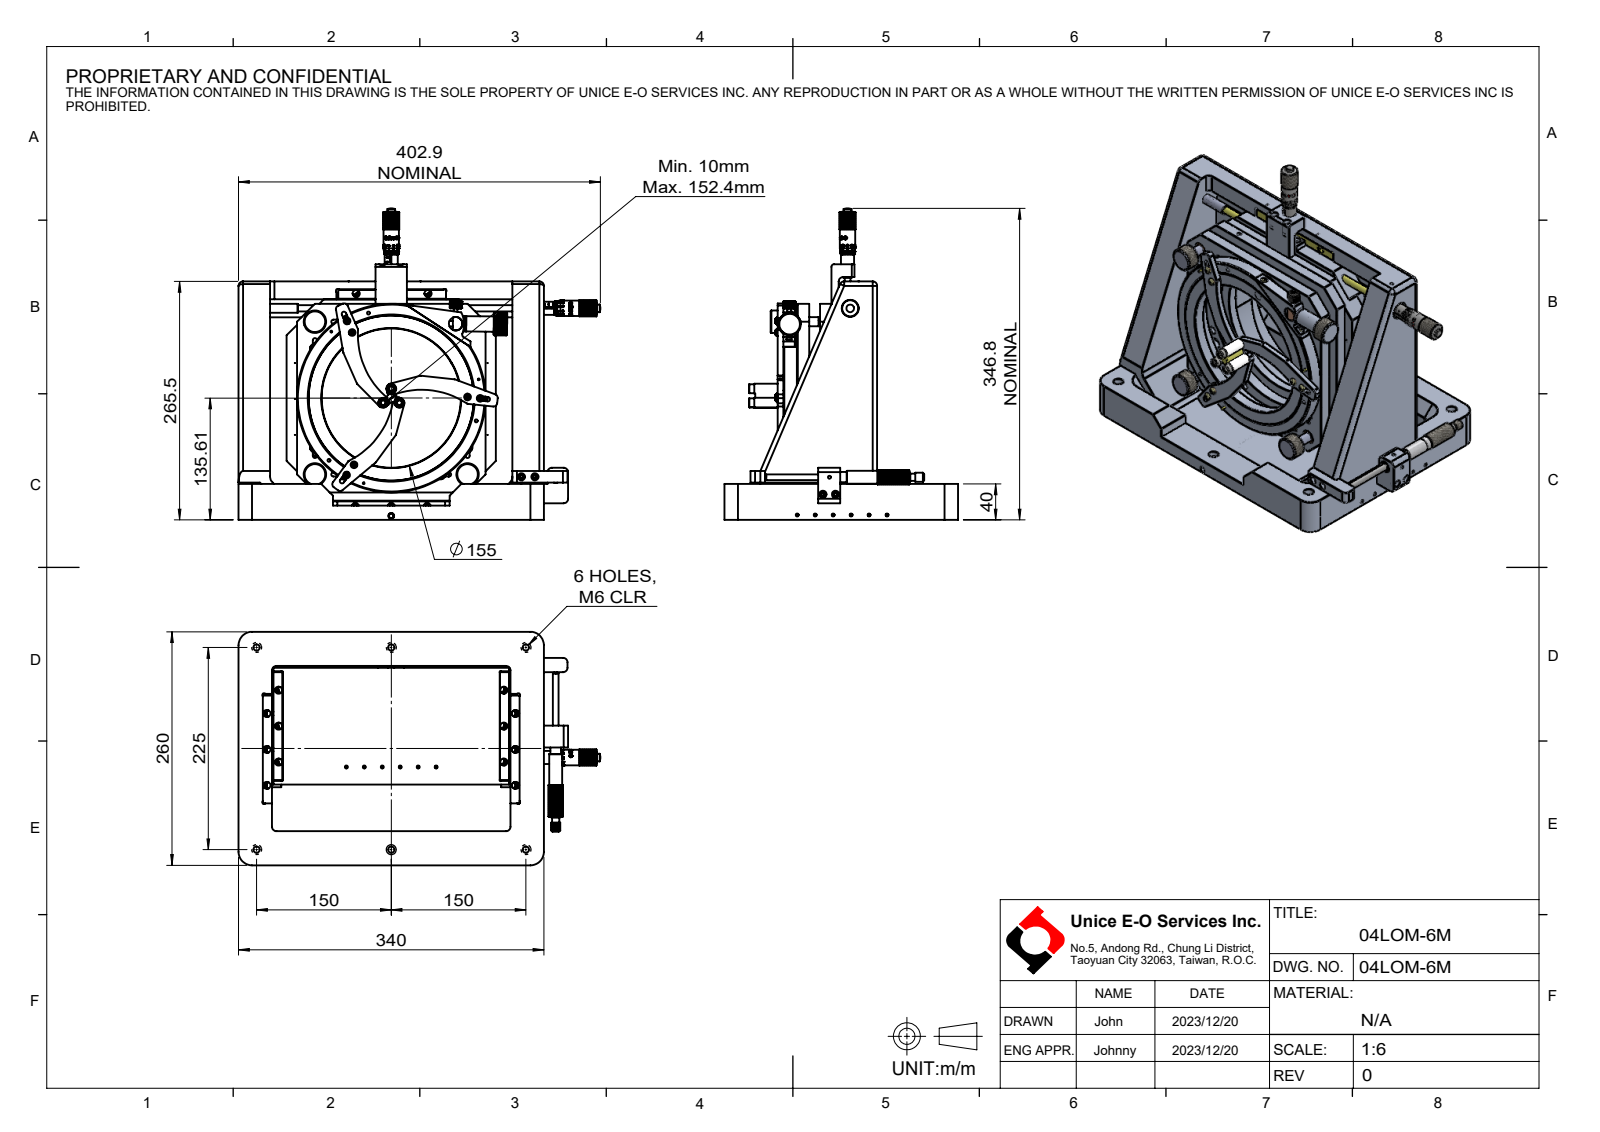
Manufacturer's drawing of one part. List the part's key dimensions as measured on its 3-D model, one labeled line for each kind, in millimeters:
Part name (STEP PRODUCT): 04LOM-6M
STEP written by: SolidWorks 2022 (CONFIG_CONTROL_DESIGN)
Units: millimetres
Bodies: 0 solids, 804 faces (343 planar, 355 cylindrical, 106 other)
Overall size (bounding box): 402.9 × 346.8 × 260
Round holes (diameter × count): ⌀8 ×29, ⌀3.3 ×20, ⌀11 ×12, ⌀7 ×6, ⌀15 ×4, ⌀6.5 ×3, ⌀4.2 ×2, ⌀4.3 ×2, ⌀178 ×2, ⌀6 ×1, ⌀7.2 ×1, ⌀7.5 ×1
Round bosses / shafts (diameter × count): ⌀4 ×14, ⌀6.5 ×9, ⌀10 ×7, ⌀7 ×6, ⌀7.5 ×5, ⌀25 ×4, ⌀11 ×3, ⌀2 ×3
Partial cylindrical surfaces — rounded edges, fillets, slot ends (radius × count): R0.1 ×22, R5 ×20, R4 ×13, R2 ×11, R2.25 ×9, R2.5 ×4, R3 ×4, R10 ×4
Main face-to-face distances: 40, 51, 38, 13, 35, 0.5, 24.7, 12.7, 27, 305
Hole centre spacings: 40, 20, 80, 98.49, 30, 60, 101.24, 139.28
